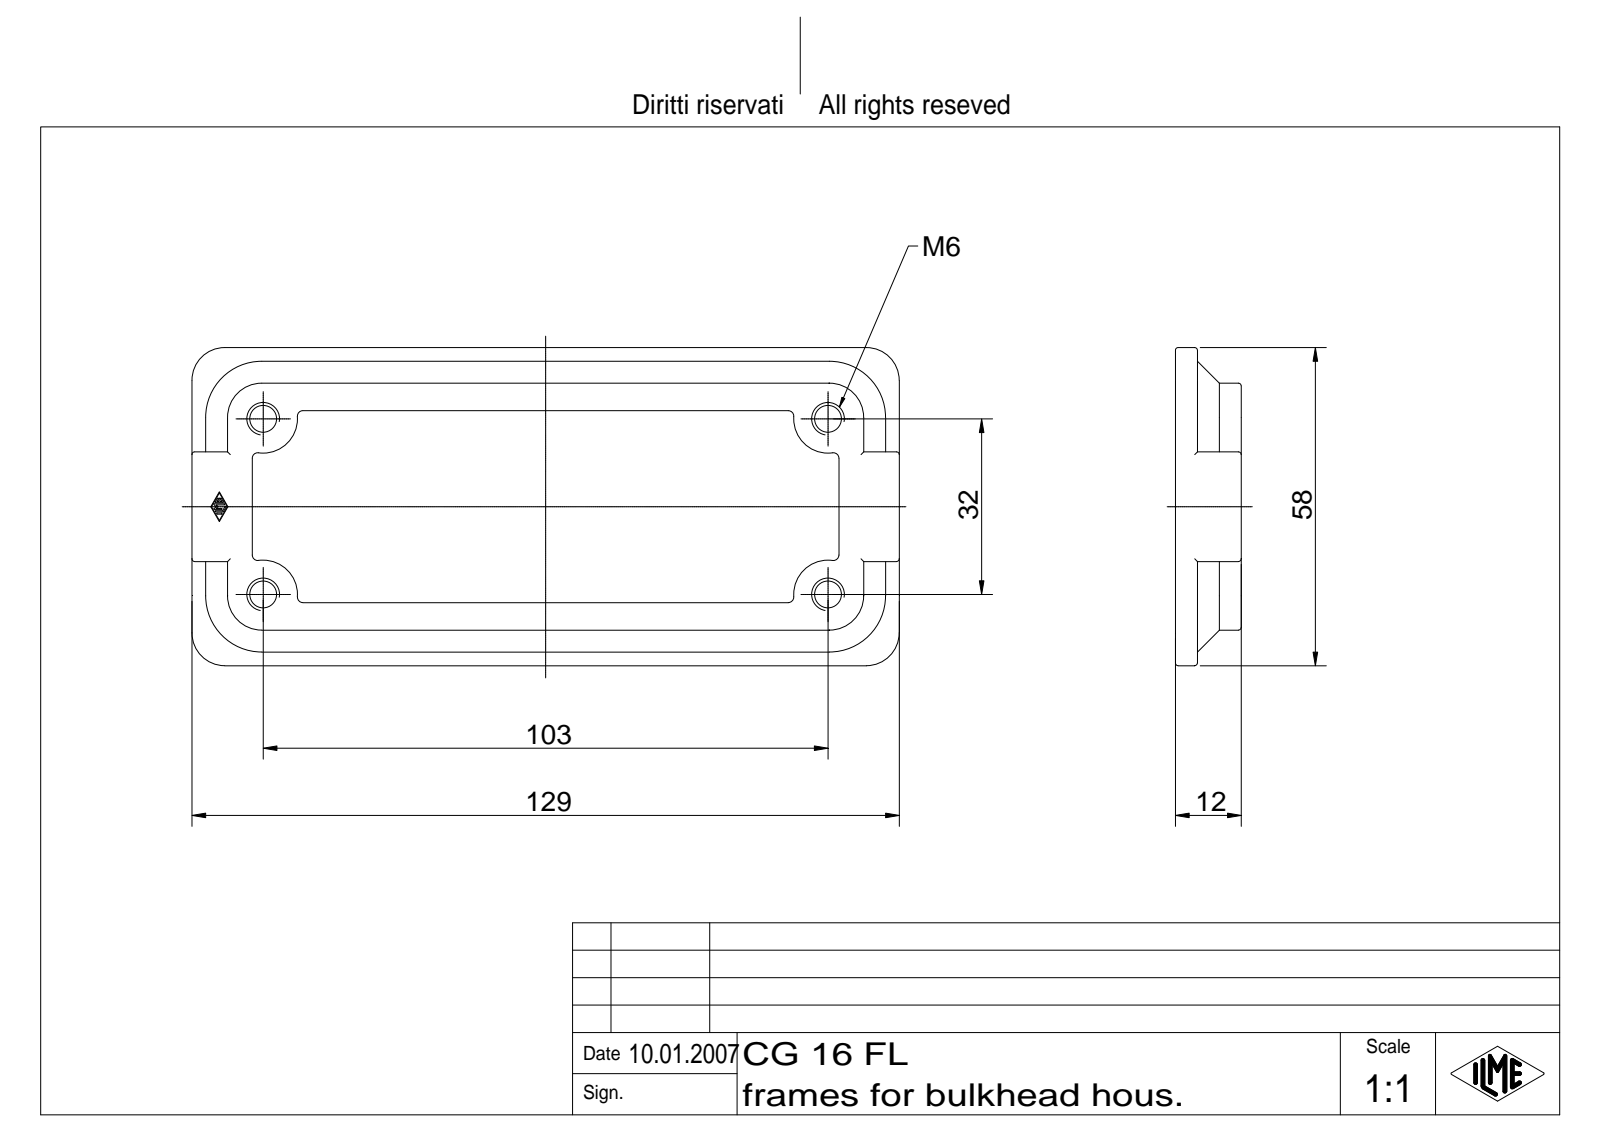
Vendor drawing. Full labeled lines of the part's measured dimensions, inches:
Part name (STEP PRODUCT): CG 16 FL
STEP written by: Autodesk Inventor 7 (AUTOMOTIVE_DESIGN)
Units: inches
Bodies: 1 solid, 215 faces (65 planar, 110 cylindrical, 40 other)
Overall size (bounding box): 5.079 × 2.283 × 0.472
Volume: 1.975 in³ · Surface area: 23.13 in²
Round holes (diameter × count): ⌀0.194 ×4
Partial cylindrical surfaces — rounded edges, fillets, slot ends (radius × count): R0.02 ×24, R0.004 ×14, R0.039 ×8, R0.246 ×8, R0.236 ×4
Main face-to-face distances: 0.472, 1.378, 0.256, 0.197, 1.575, 0.157, 0.315, 0.453, 1.831, 2.028
Hole centre spacings: 1.26, 4.055, 4.246
